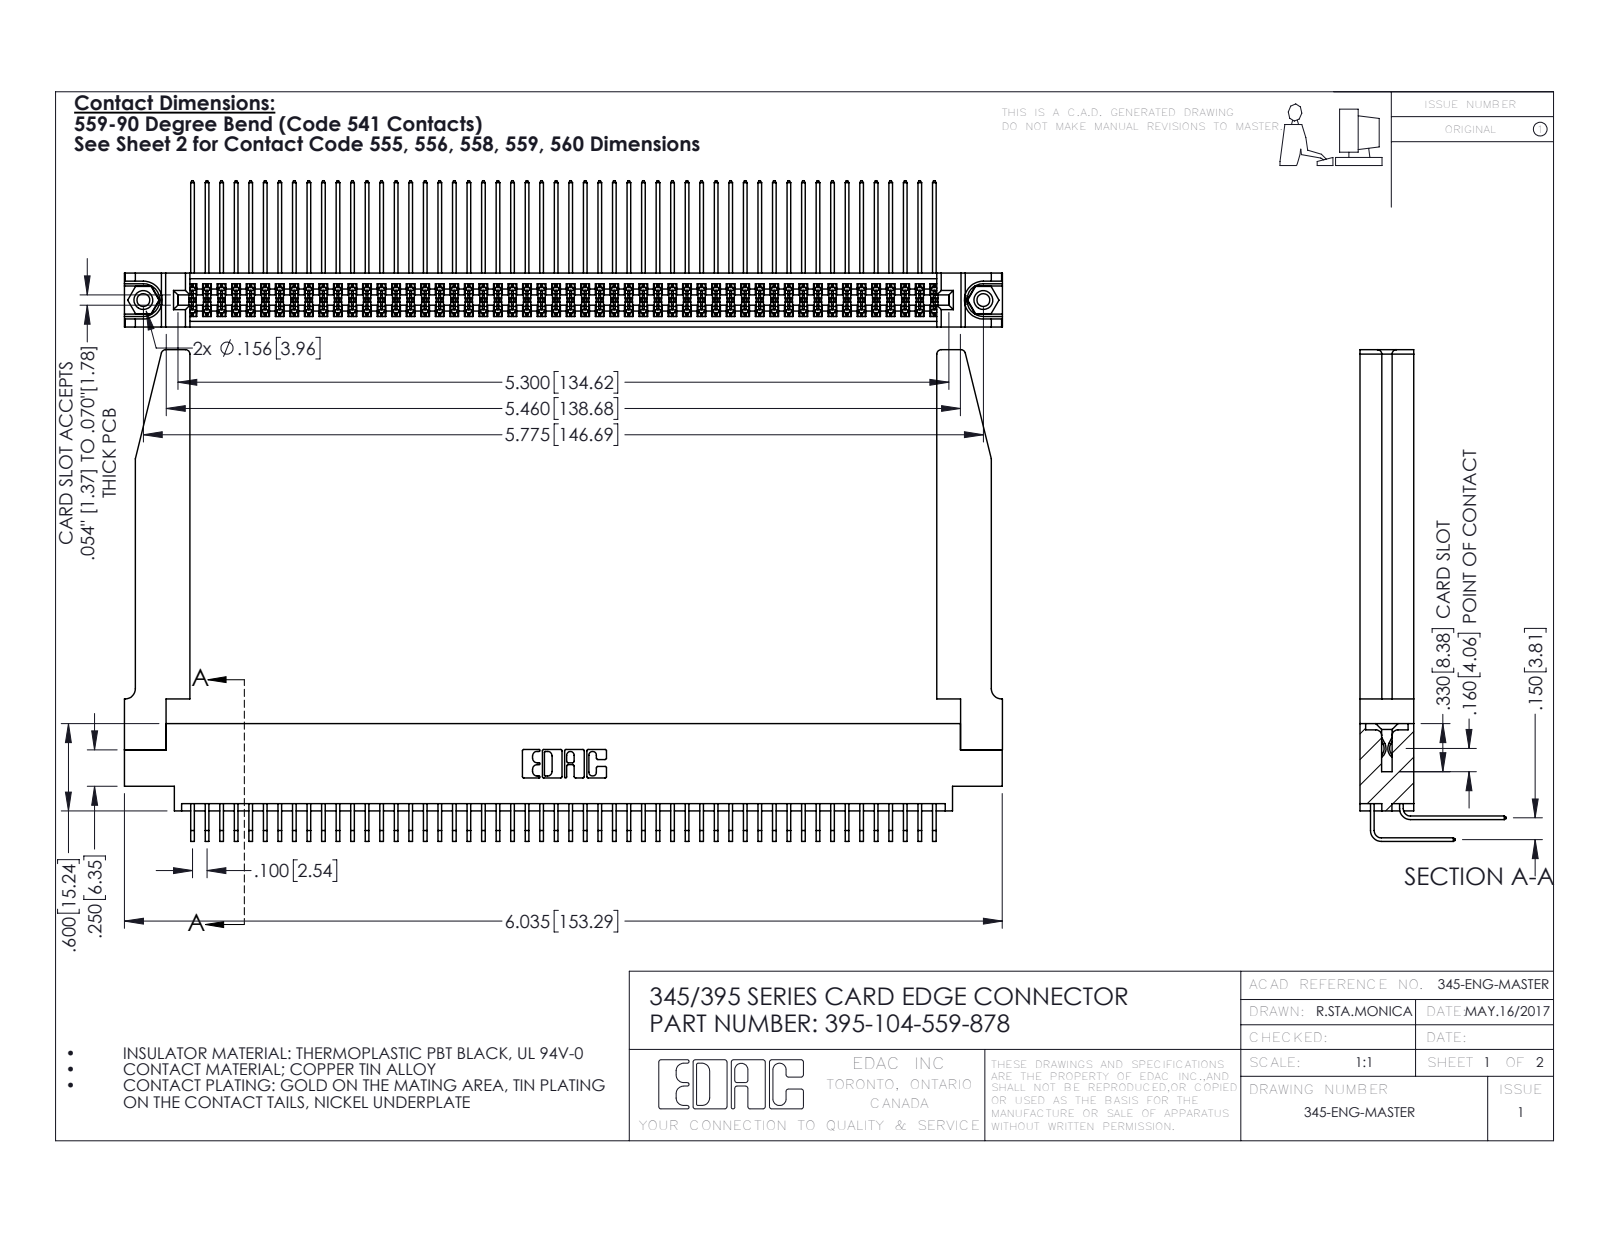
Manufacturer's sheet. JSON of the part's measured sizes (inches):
{"part_name": "345-292-001_559 Tail - 2; 395-104-559-878; 345-220-078_345-220-078; 345 Part_0.170 Offset - 0.156 Dia-TH (+2 more)", "step_written_by": "SolidWorks 2016 (CONFIG_CONTROL_DESIGN)", "units": "inches", "bodies": {"solids": 109, "faces": 5772, "planar": 3866, "cylindrical": 1854, "other": 52}, "overall_size": [6.036, 3.379, 1.005], "volume_in3": 1.418, "surface_area_in2": 50.95, "round_holes": [[0.089, 2], [0.125, 2], [0.156, 2], [0.064, 1]], "round_bosses_or_shafts": [[0.155, 2]], "partial_cylinders_radius": [[0.006, 156], [0.01, 22], [0.03, 8], [0.007, 6], [0.031, 6], [0.026, 3], [0.014, 2], [0.019, 2]], "face_to_face_distances": [0.072, 0.37, 0.298, 0.098, 0.272, 0.025, 0.2, 0.225, 0.15, 0.175], "hole_center_spacings": [0.27, 5.539, 5.775]}
